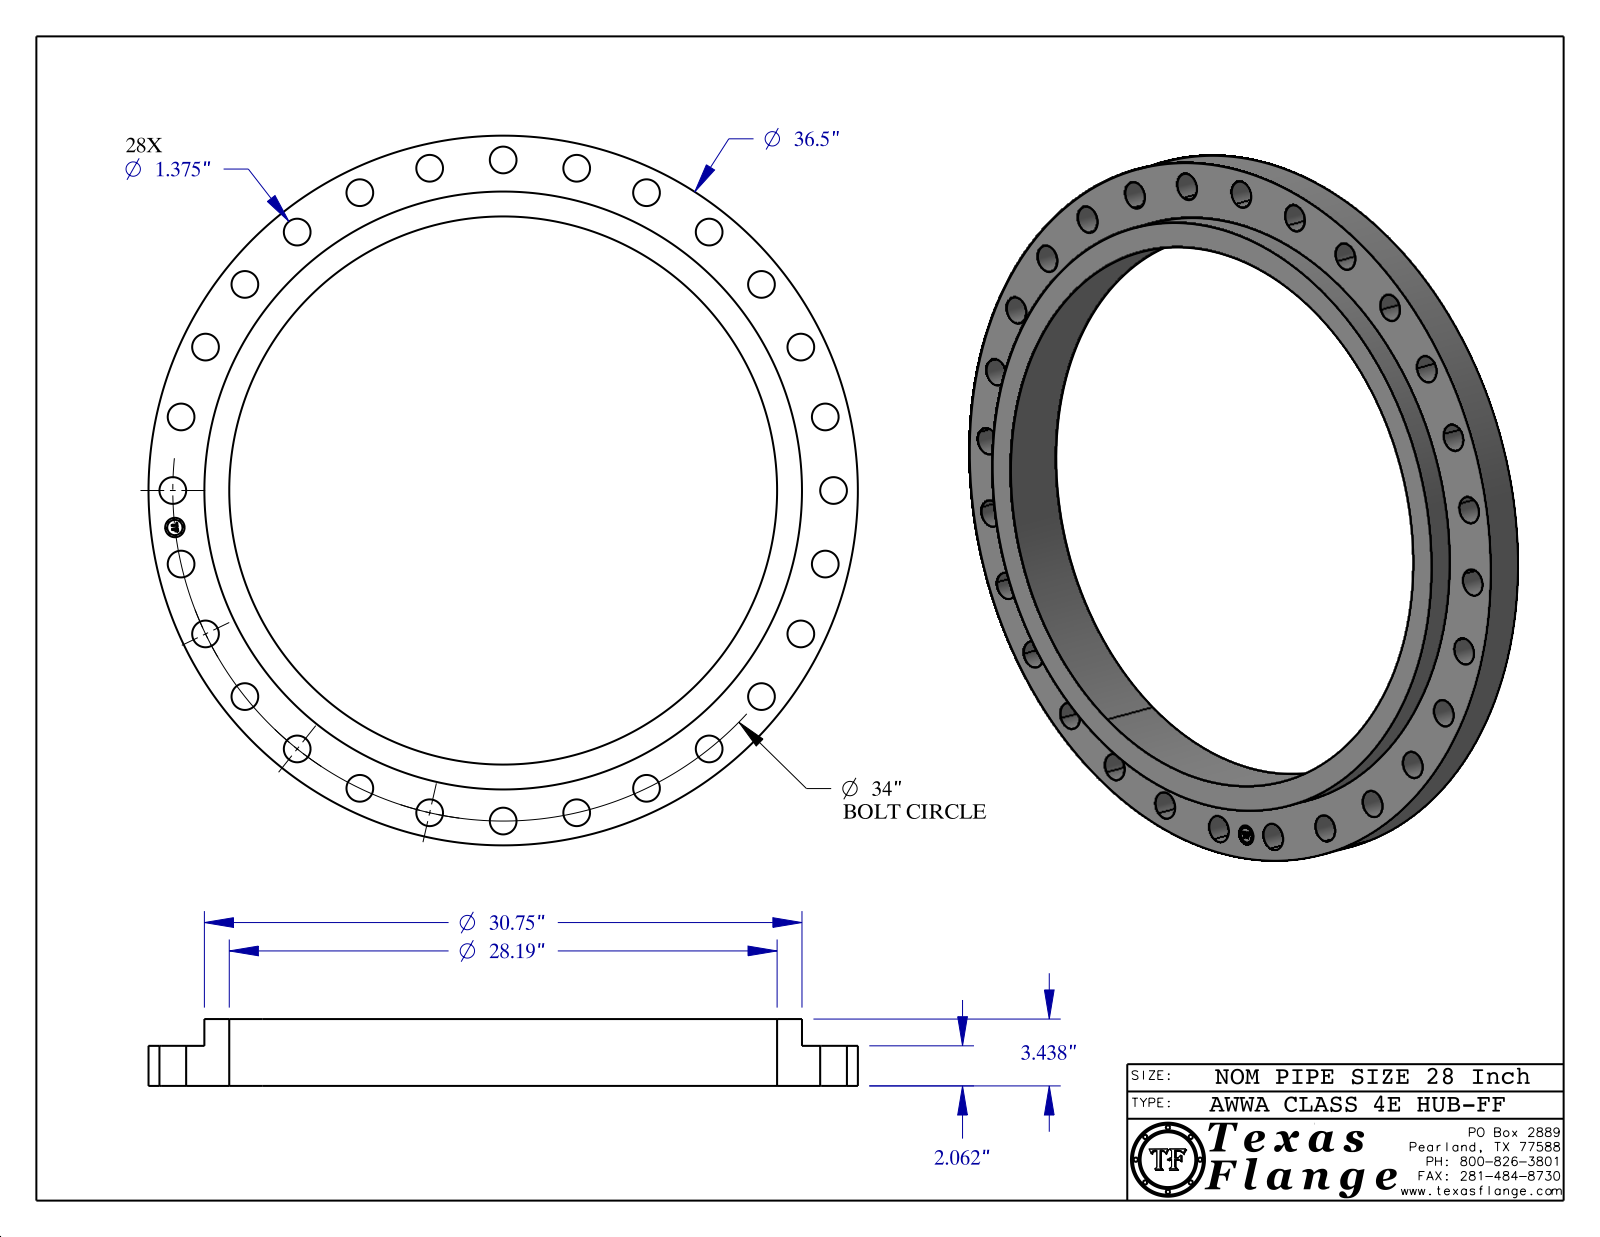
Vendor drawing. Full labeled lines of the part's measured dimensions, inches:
Part name (STEP PRODUCT): AWWA Class 4E-HUB-FF
STEP written by: CATIA V5 STEP AP214 (AUTOMOTIVE_DESIGN)
Units: inches
Bodies: 1 solid, 450 faces (368 planar, 82 cylindrical, 0 other)
Overall size (bounding box): 36.5 × 36.5 × 3.438
Volume: 947.9 in³ · Surface area: 1 685 in²
Round holes (diameter × count): ⌀1.375 ×28, ⌀1 ×1, ⌀28.19 ×1
Round bosses / shafts (diameter × count): ⌀0.061 ×8, ⌀36.5 ×1, ⌀30.75 ×1, ⌀0.788 ×1
Main face-to-face distances: 2.062, 3.438, 1.376, 0.015, 2.047, 1.391, 0.298, 0.293, 0.054, 0.193
Hole centre spacings: 3.807, 7.566, 30.633, 33.786, 17, 11.23, 18.089, 21.198
